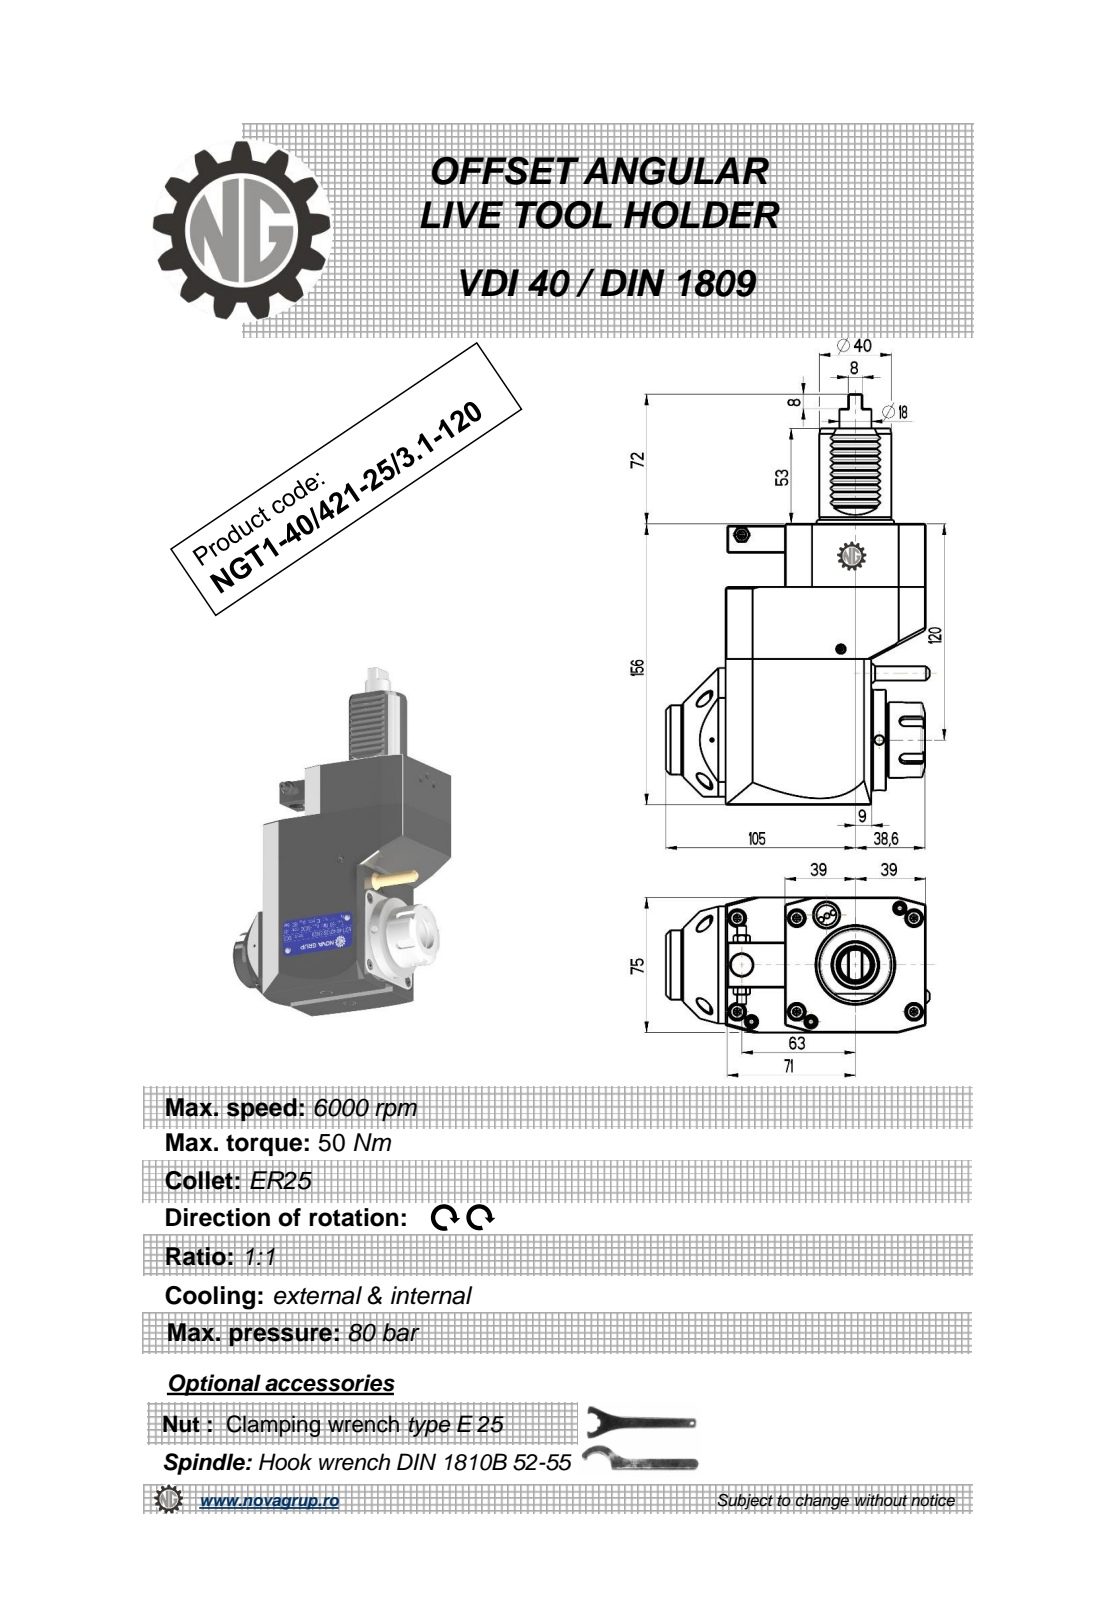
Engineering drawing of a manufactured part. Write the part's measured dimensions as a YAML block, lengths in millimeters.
part_name: "NGT1_40_421_25_3_1_120"
step_written_by: "PRO/ENGINEER BY PARAMETRIC TECHNOLOGY CORPORATION, 2010280 (CONFIG_CONTROL_DESIGN)"
units: millimeters
bodies: {solids: 1, faces: 441, planar: 207, cylindrical: 87, other: 147}
overall_size: [228, 146.14, 75]
volume: 1198000
surface_area: 88955
round_holes:
  - {diameter: 5, count: 3}
  - {diameter: 3, count: 1}
  - {diameter: 4.2, count: 1}
  - {diameter: 9.5, count: 1}
  - {diameter: 12, count: 1}
  - {diameter: 20.3, count: 1}
round_bosses_or_shafts:
  - {diameter: 56, count: 1}
  - {diameter: 43, count: 1}
  - {diameter: 42, count: 1}
  - {diameter: 40, count: 1}
  - {diameter: 38.5, count: 1}
  - {diameter: 33, count: 1}
  - {diameter: 17.8, count: 1}
  - {diameter: 11.2, count: 1}
partial_cylinders:
  - {radius: 0.26, count: 12}
  - {radius: 0.3, count: 10}
  - {radius: 0.22, count: 6}
  - {radius: 3, count: 5}
  - {radius: 0.8, count: 2}
  - {radius: 0.5, count: 1}
  - {radius: 40, count: 1}
face_to_face_distances: [75, 156, 111, 33, 35, 121, 81, 30, 48, 78]
hole_center_spacings: [40.93, 76.25, 77.5, 112.5, 137.15]
